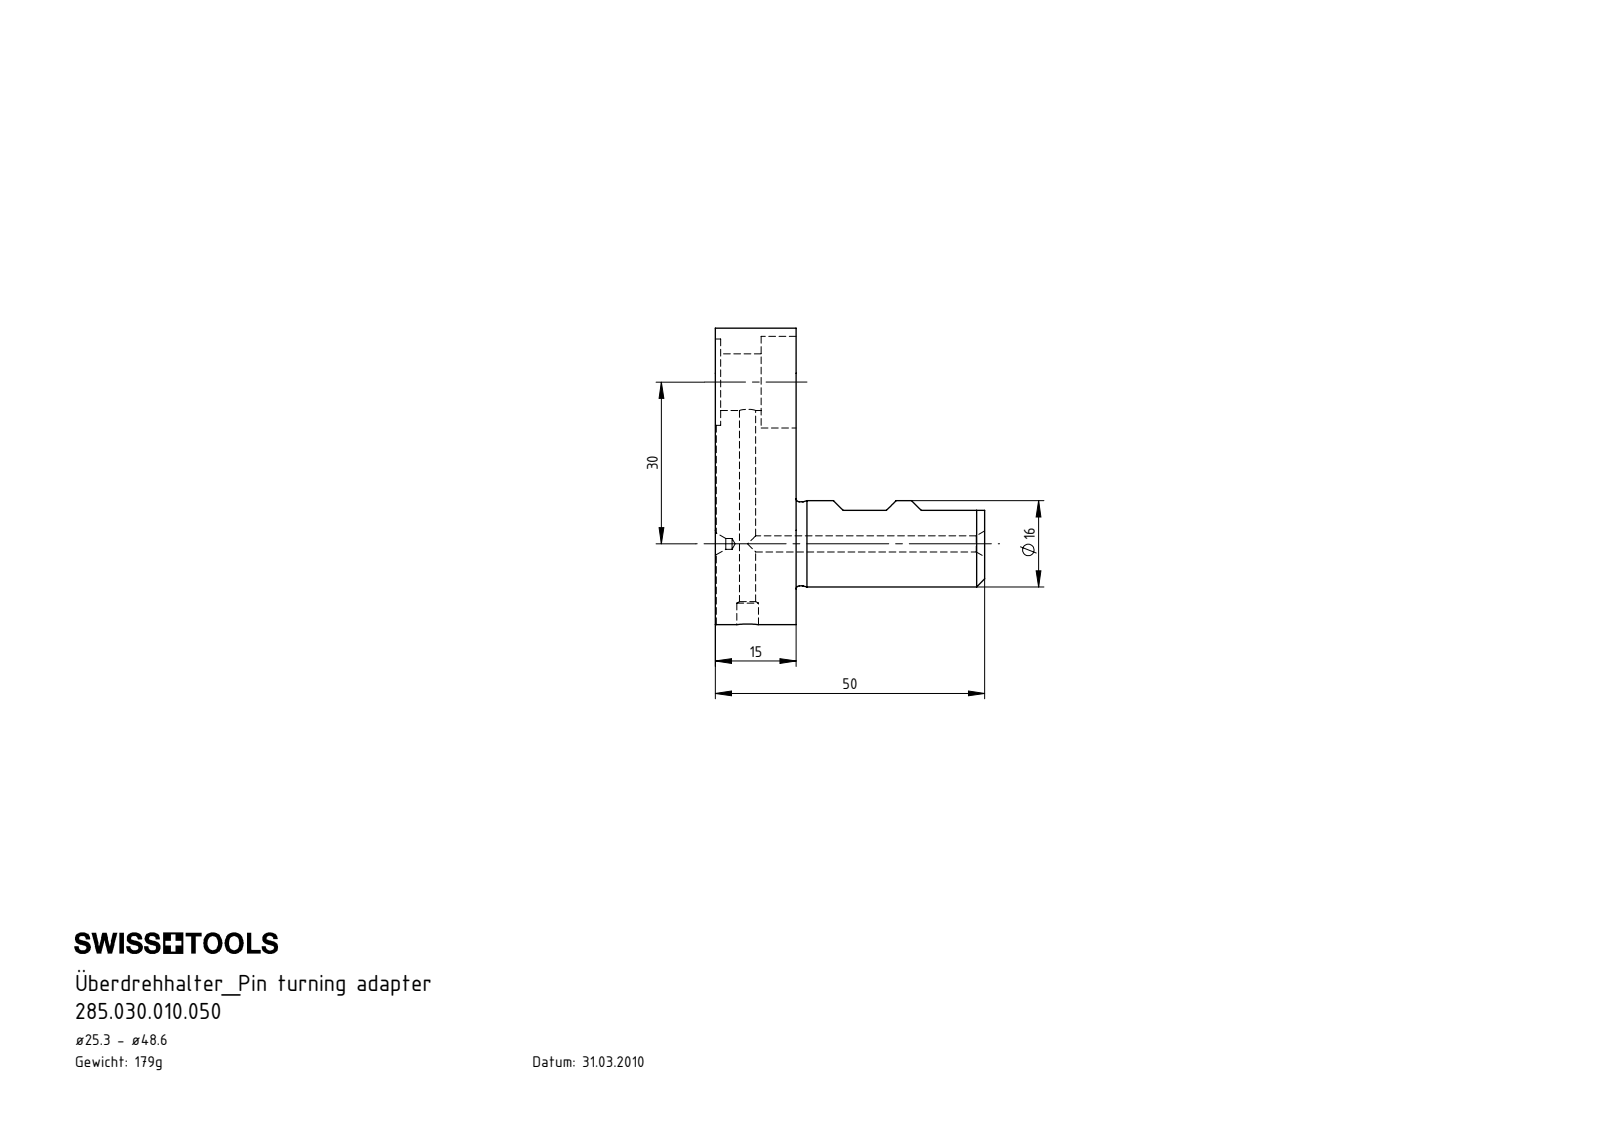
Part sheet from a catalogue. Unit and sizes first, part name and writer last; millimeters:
Units: millimetres
Overall size (bounding box): 76 × 55 × 30
Round holes (diameter × count): ⌀3 ×3, ⌀2 ×1, ⌀2.05 ×1, ⌀2.8 ×1, ⌀3.85 ×1, ⌀4 ×1, ⌀8.2 ×1, ⌀10.5 ×1, ⌀17 ×1
Round bosses / shafts (diameter × count): ⌀16 ×2, ⌀15.6 ×1, ⌀10 ×1, ⌀3.4 ×1, ⌀2.5 ×1
Partial cylindrical surfaces — rounded edges, fillets, slot ends (radius × count): R0.21 ×6, R0.36 ×5, R0.36 ×1, R1.5 ×1, R1.8 ×1, R2 ×1, R10 ×1, R15 ×1
Main face-to-face distances: 15, 8.5, 7.5, 14, 6.5, 1, 6, 0.5, 11, 35
Hole centre spacings: 30
Volume: 28 462 mm³ · Surface area: 11 162 mm²
Bodies: 5 solids, 208 faces (67 planar, 61 cylindrical, 80 other)
Part name (STEP PRODUCT): CCMT060204; WCA-ER2.001.006_A; HS0-A32.K11.027_B; UH1-ER1.001.016_A (+3 more)
STEP written by: SolidWorks 2017 (CONFIG_CONTROL_DESIGN)
